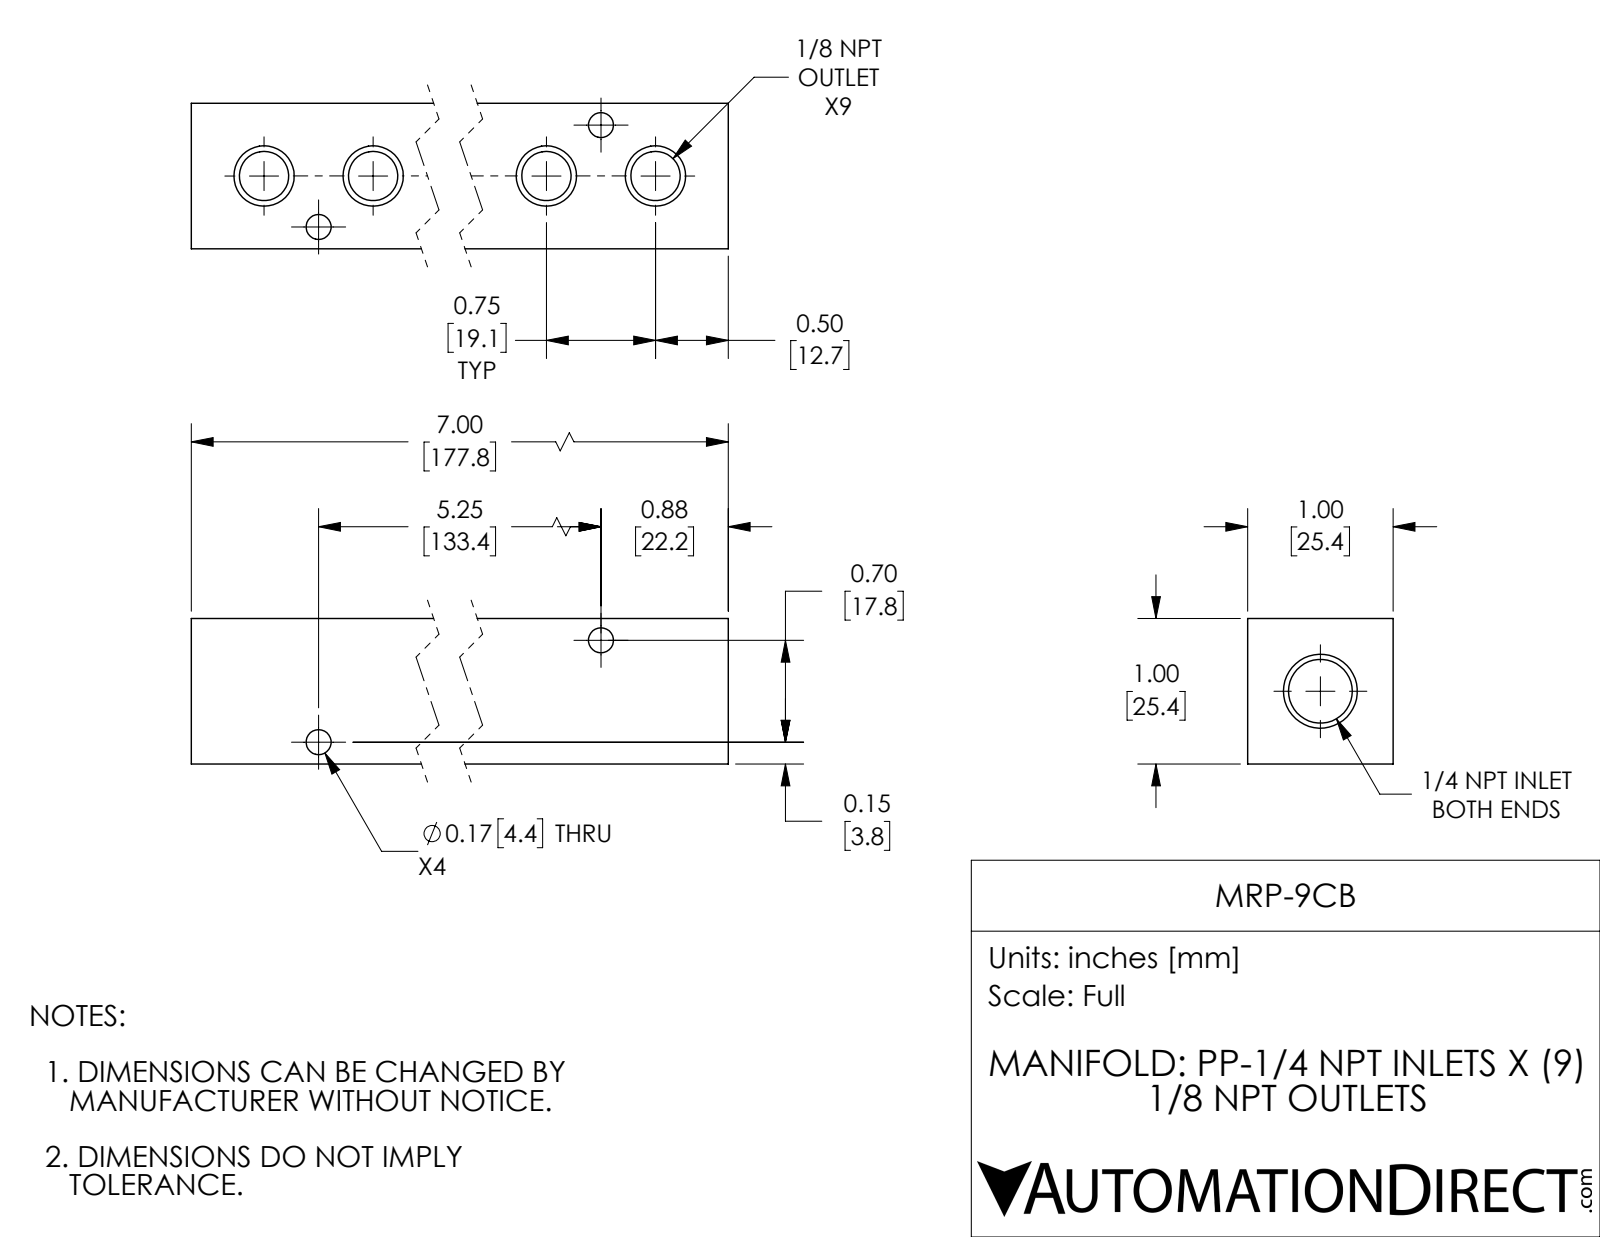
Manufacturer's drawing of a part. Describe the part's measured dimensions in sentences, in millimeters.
The part is named "MRP-9CB". Its 3-D file was written by "SolidWorks 2018 (AUTOMOTIVE_DESIGN)". It is 1 solid with 64 faces: 6 planar, 36 cylindrical and 22 other. Overall it measures 177.8 by 25.4 by 25.4 millimeters. Its volume is 91 880 cubic millimeters and its surface area 27 210 square millimeters. Round holes: 9 of diameter 8.6, 4 of diameter 4.4, 1 of diameter 11.1. The main face-to-face distances are 25.4, 177.8. The hole center spacings are 19.1, 38.1, 57.2, 76.2, 13, 95.3, 114.3, 133.4.
